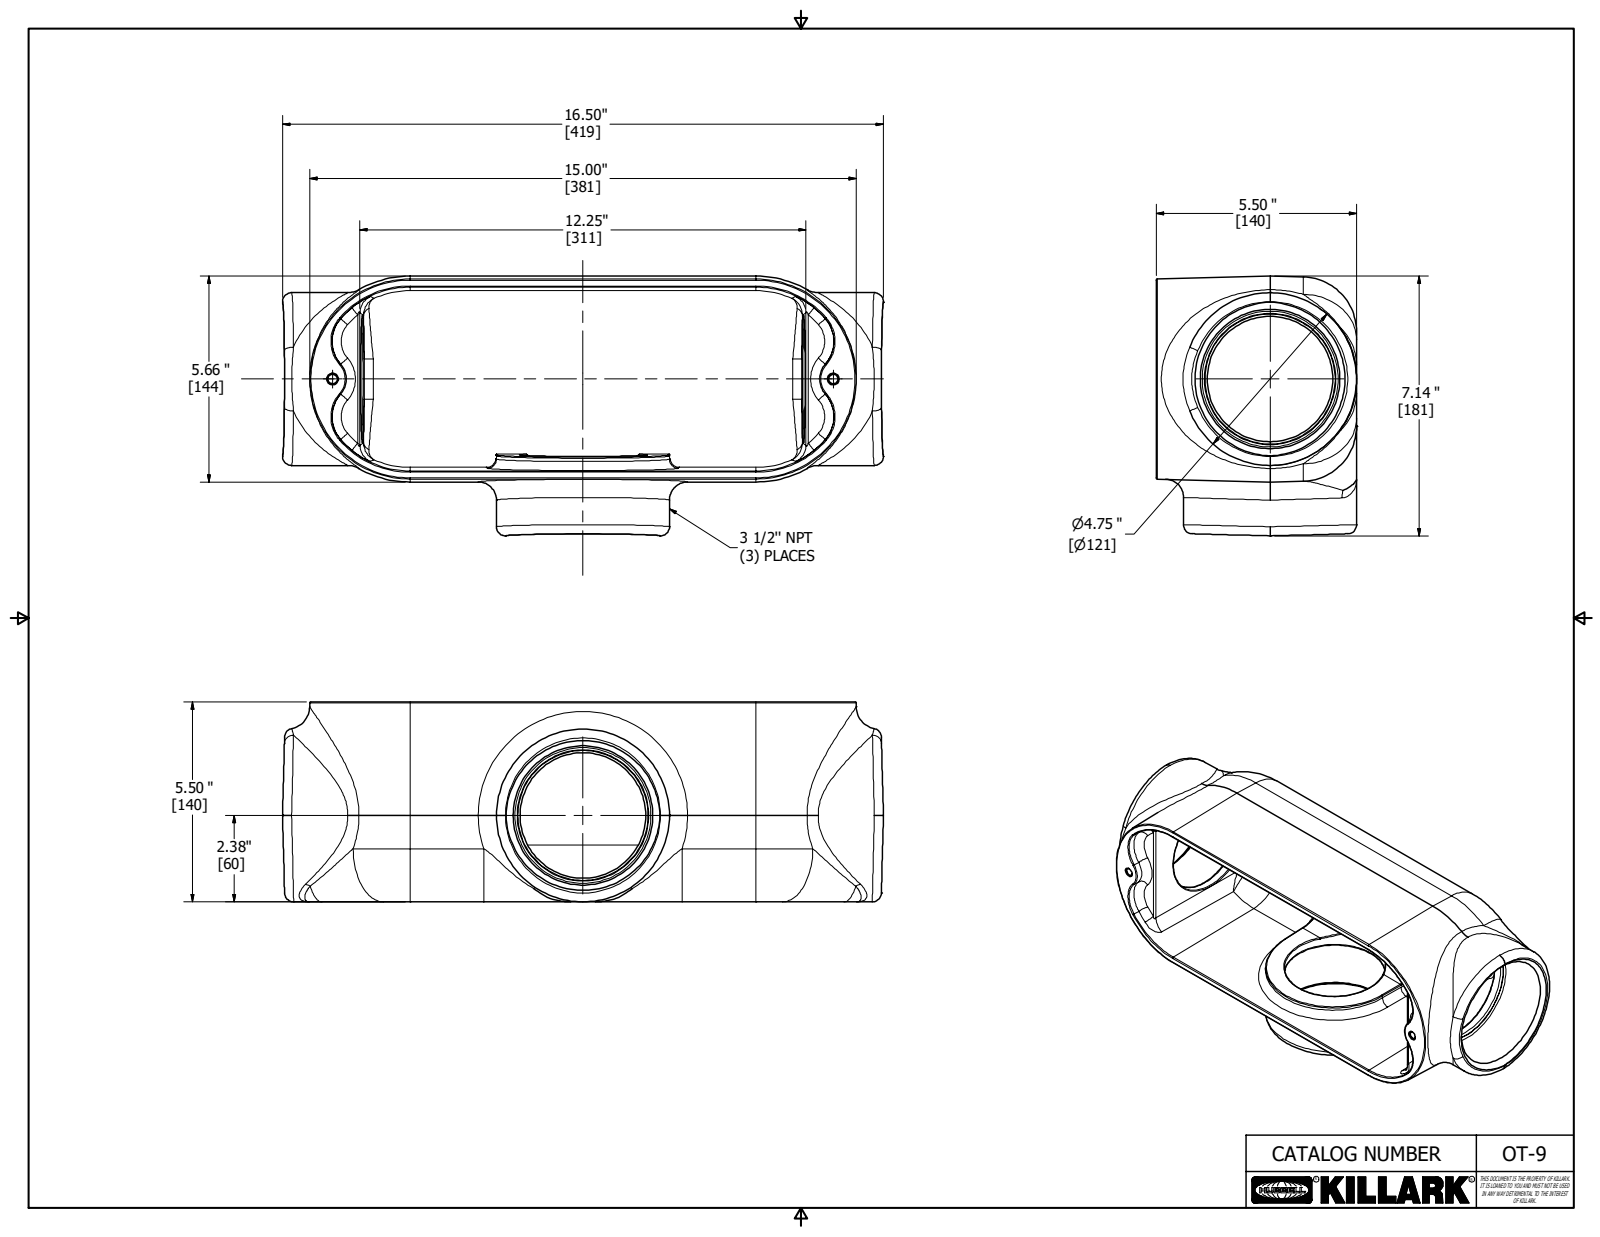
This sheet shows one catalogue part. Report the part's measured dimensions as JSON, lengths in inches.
{"part_name": "10756-1 OT-9", "step_written_by": "Autodesk Inventor 2018 (AUTOMOTIVE_DESIGN)", "units": "inches", "bodies": {"solids": 1, "faces": 1383, "planar": 709, "cylindrical": 79, "other": 595}, "overall_size": [16.5, 7.144, 5.5], "volume_in3": 110.6, "surface_area_in2": 551.1, "round_holes": [[3.448, 2], [0.502, 1]], "round_bosses_or_shafts": [[4.75, 2], [0.752, 1]], "partial_cylinders_radius": [[0.031, 28], [0.25, 4], [1.281, 3], [0.03, 2], [0.062, 2], [0.625, 2], [1.5, 2], [0.031, 1]], "face_to_face_distances": [5.281, 0.313, 0.382, 5.663, 5.5, 5.187, 0.063, 0.375, 5.125, 0.031]}
